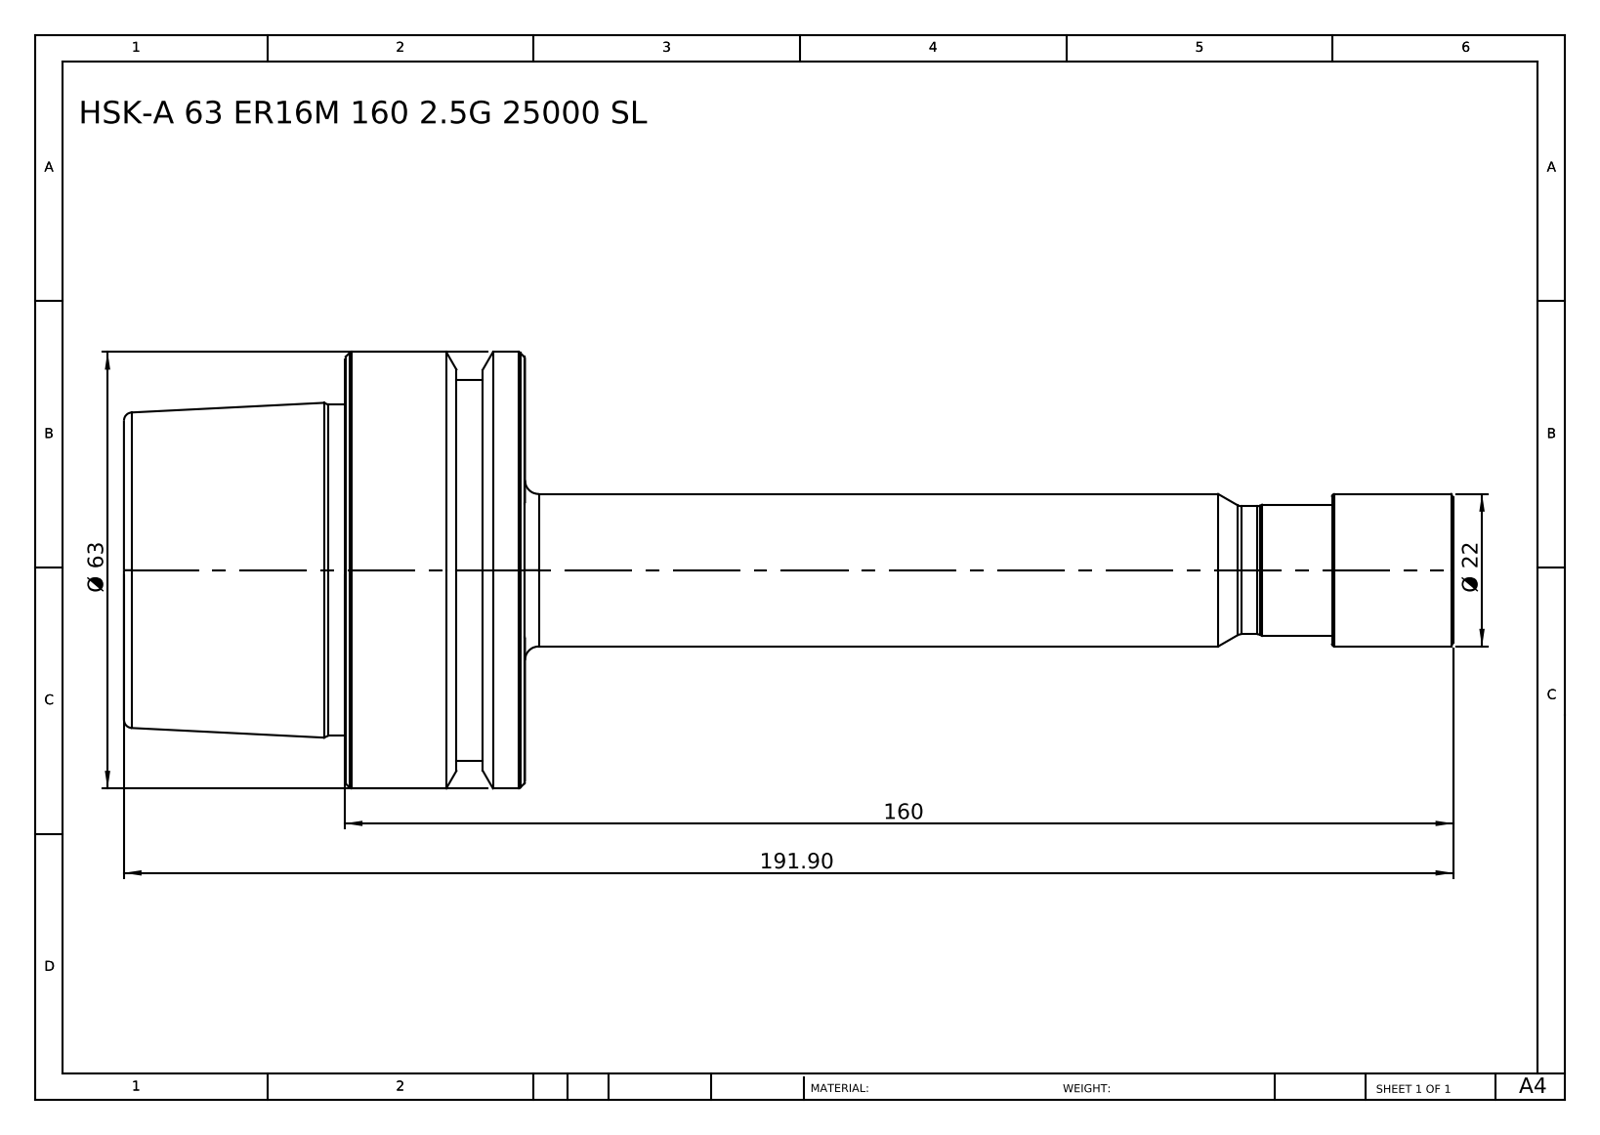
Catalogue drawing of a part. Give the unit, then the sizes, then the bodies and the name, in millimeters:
Units: millimetres
Overall size (bounding box): 191.9 × 63 × 63
Round bosses / shafts (diameter × count): ⌀63 ×1, ⌀55 ×1, ⌀47.78 ×1, ⌀22 ×1, ⌀18.9 ×1, ⌀18.5 ×1
Main face-to-face distances: 57.9, 26, 31.9, 134, 160, 191.9, 143.9, 9.9, 16.1, 48
Volume: 182 050 mm³ · Surface area: 25 808 mm²
Bodies: 1 solid, 68 faces (7 planar, 16 cylindrical, 45 other)
Part name (STEP PRODUCT): HSK-A 63 ER16M 160 2.5G 25000 SL
STEP written by: SolidWorks 2014 (CONFIG_CONTROL_DESIGN)
